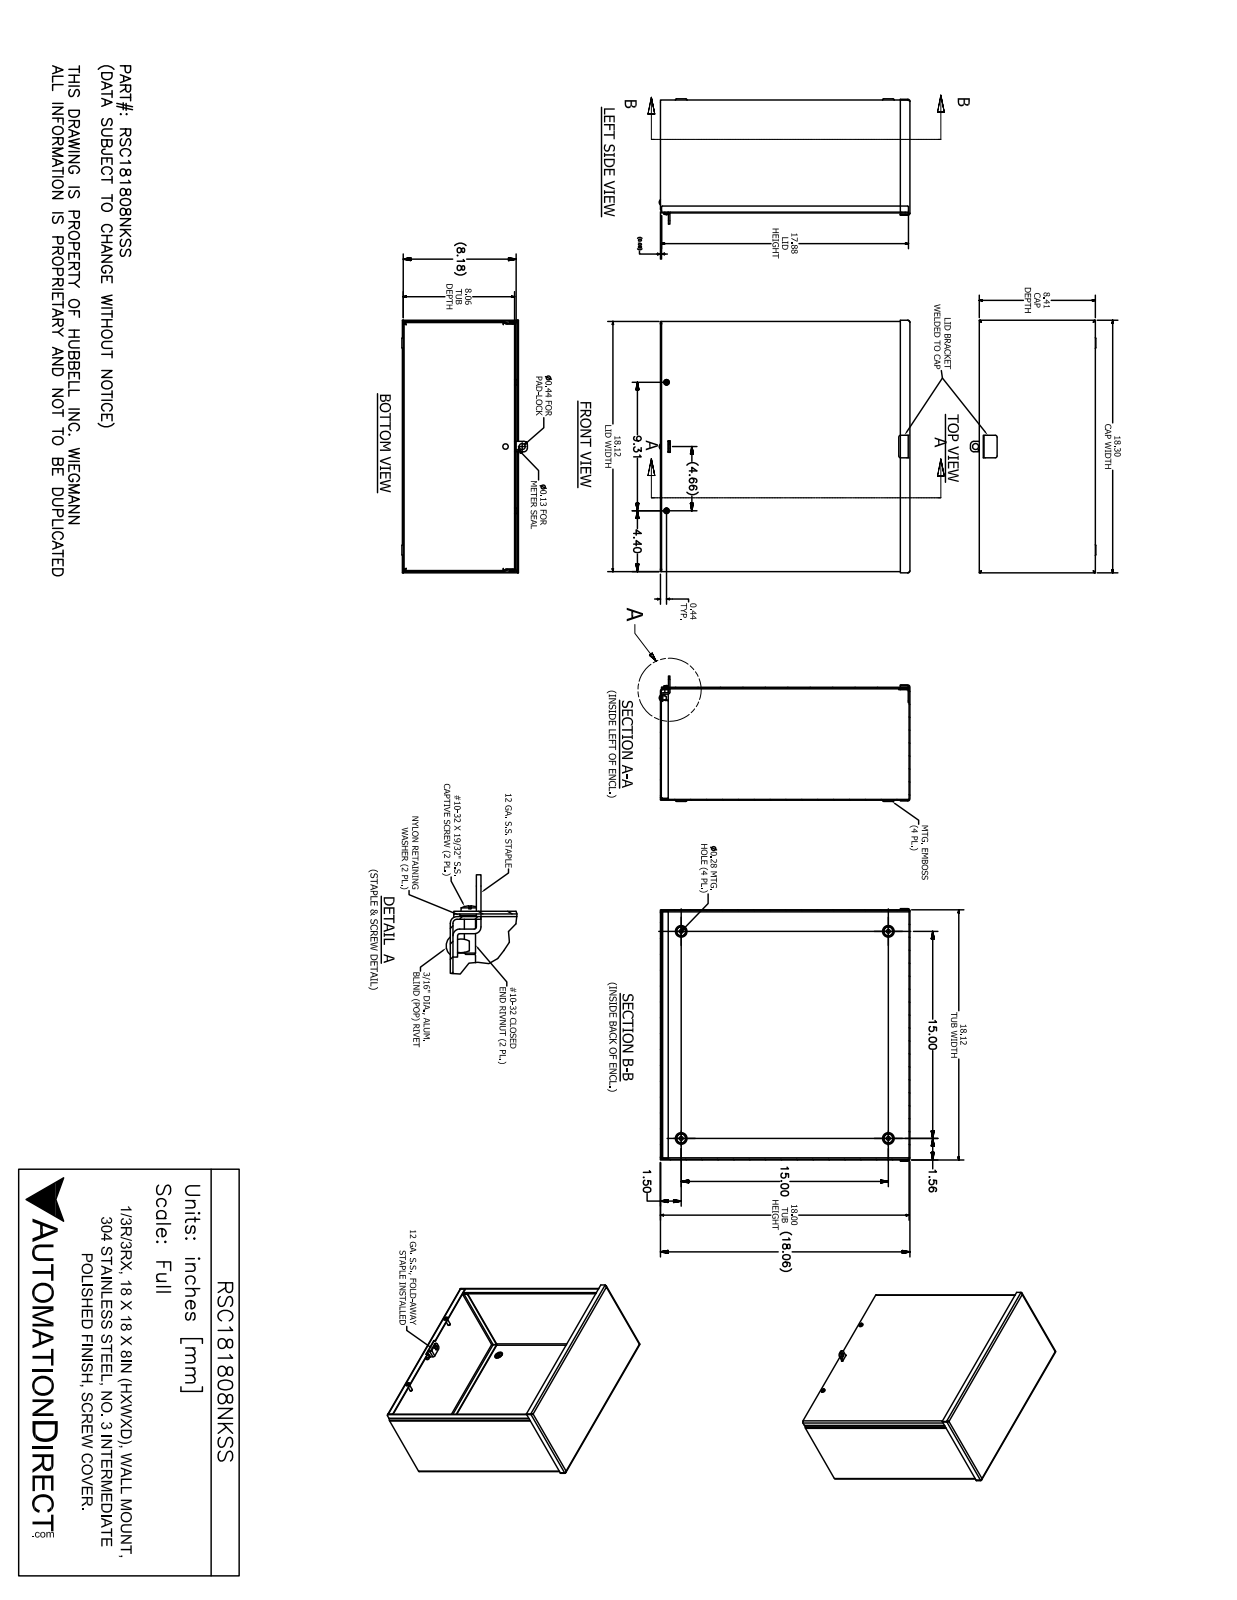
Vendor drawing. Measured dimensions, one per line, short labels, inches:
name: RSC181808NKSS
written by: SolidWorks 2017 (AUTOMOTIVE_DESIGN)
unit: in
bodies: 13 solids, 383 faces (199 planar, 99 cylindrical, 85 other)
size: 18.299 × 18.149 × 9.084
volume: 77.33 in³; area: 2 639 in²
holes: 4× ⌀0.25, 4× ⌀0.281, 2× ⌀0.156, 2× ⌀0.196, 2× ⌀0.257, 2× ⌀0.278, 1× ⌀0.125, 1× ⌀0.198, 1× ⌀0.201, 1× ⌀0.437
bosses: 2× ⌀0.453, 2× ⌀0.406, 2× ⌀0.248, 2× ⌀0.167, 1× ⌀0.187
rounds: 17× R0.094, 17× R0.153, 6× R0.031, 4× R0.125, 4× R0.25, 3× R0.062, 2× R0.047, 2× R0.05
face distances: 0.059, 8.117, 18, 18.059, 8.176, 8.058, 17.941, 18.118, 0.117, 0.059
hole spacings: 15, 3.036, 3.047, 9.313, 12.203, 12.206, 16.312, 16.343
